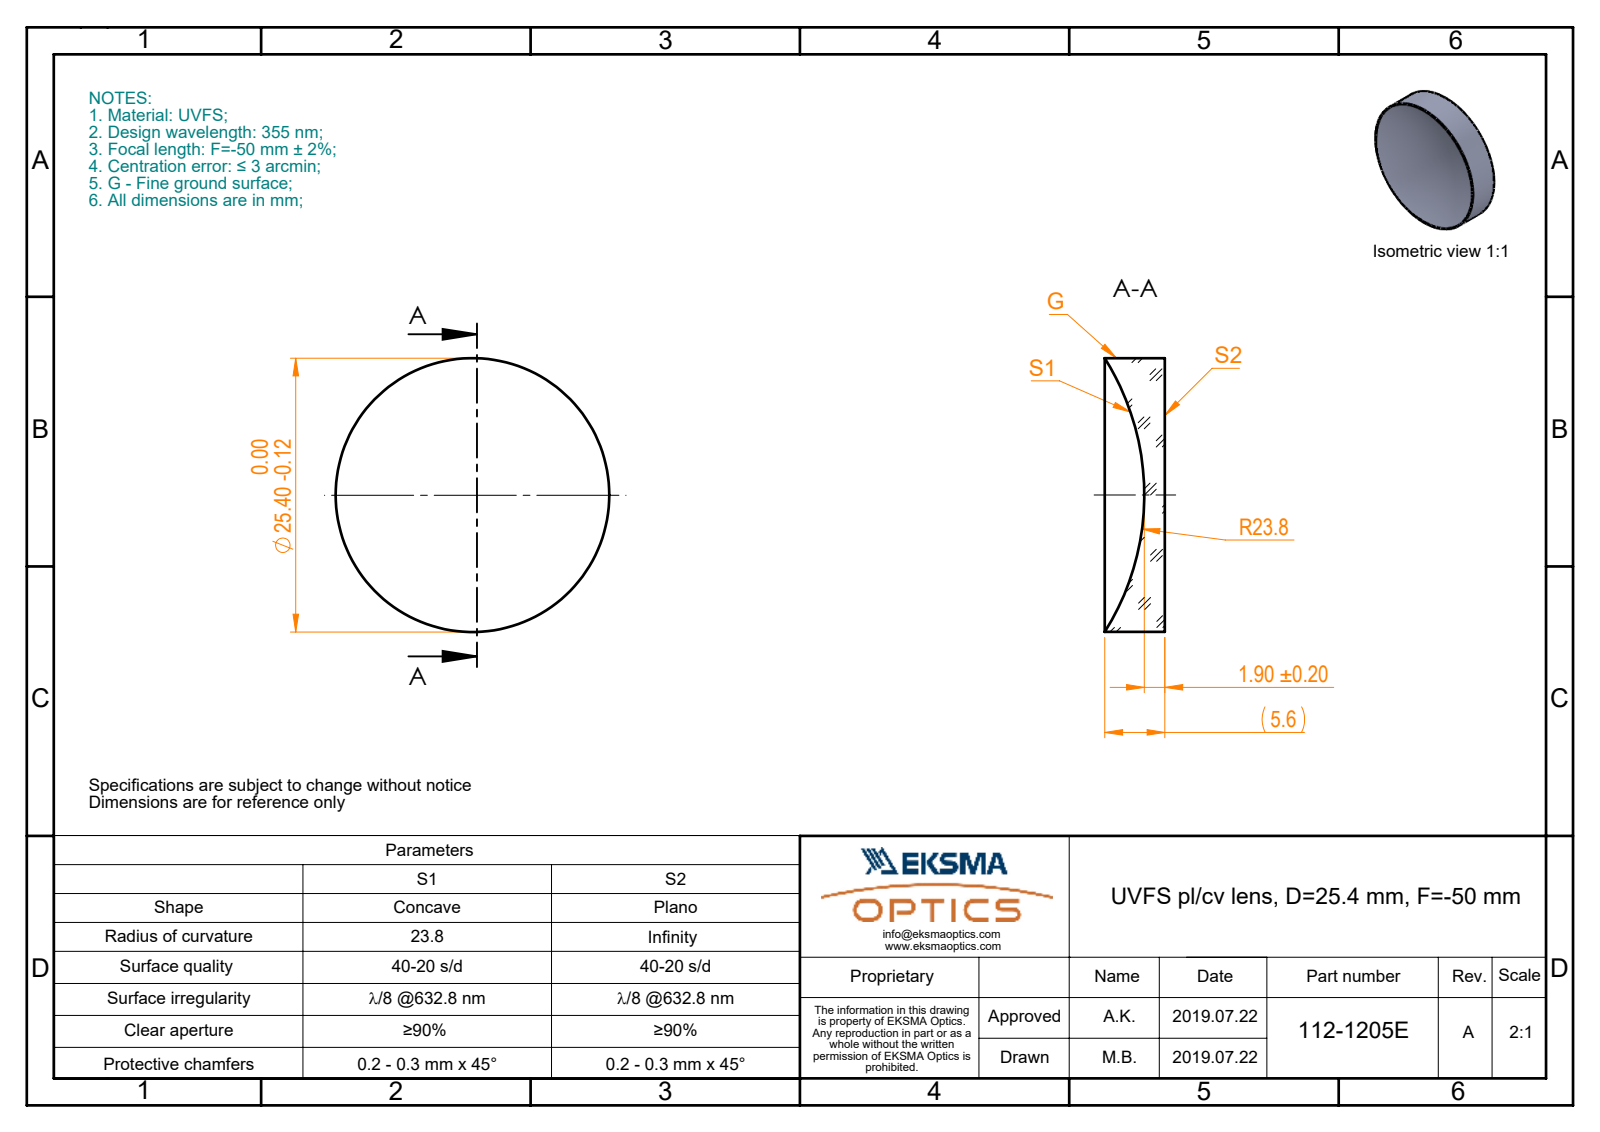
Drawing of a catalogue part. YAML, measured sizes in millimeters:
part_name: "112-1205E UVFS pl-cv 12.7 F-50"
step_written_by: "SolidWorks 2017 (CONFIG_CONTROL_DESIGN)"
units: millimeters
bodies: {solids: 1, faces: 5, planar: 1, cylindrical: 2, other: 2}
overall_size: [25.4, 25.4, 5.57]
volume: 1867
surface_area: 1500
round_bosses_or_shafts:
  - {diameter: 25.4, count: 1}
